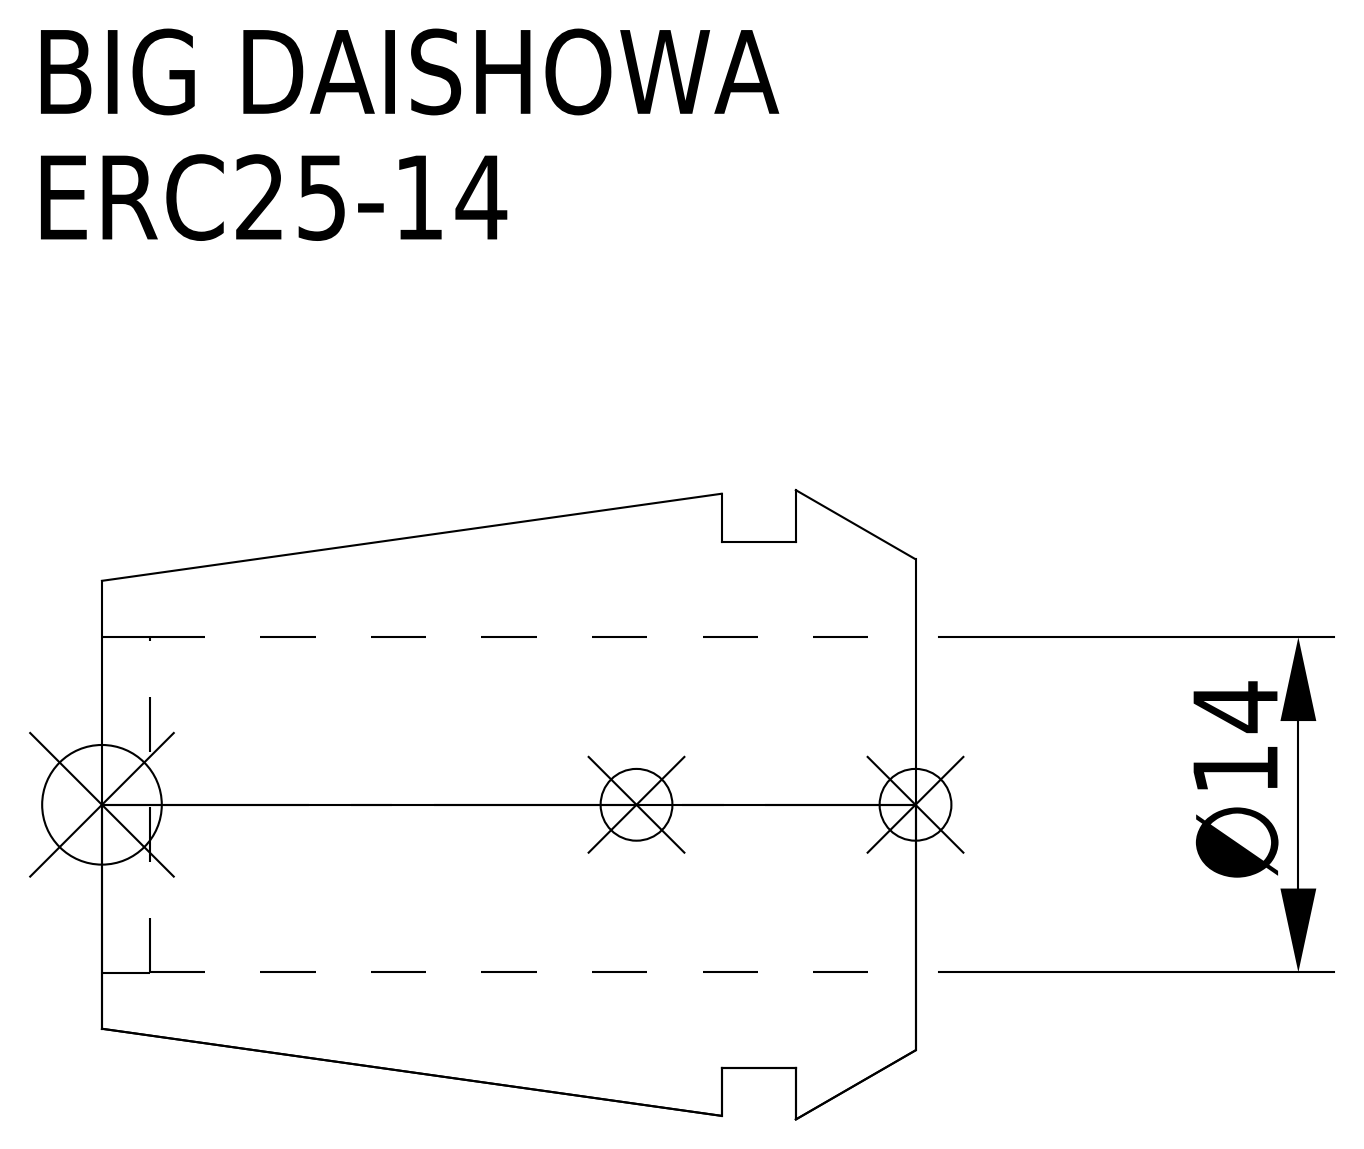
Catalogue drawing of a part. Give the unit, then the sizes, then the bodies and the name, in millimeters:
Units: millimetres
Overall size (bounding box): 34 × 26.3 × 26.3
Round holes (diameter × count): ⌀14 ×1, ⌀14.05 ×1
Round bosses / shafts (diameter × count): ⌀22 ×1
Main face-to-face distances: 5, 8.1, 3.1, 34, 29, 25.9, 32, 27, 23.9, 2
Volume: 8 367 mm³ · Surface area: 4 584 mm²
Bodies: 1 solid, 15 faces (5 planar, 6 cylindrical, 4 other)
Part name (STEP PRODUCT): ERC25-14
STEP written by: CREO PARAMETRIC BY PTC INC, 2016380 (AUTOMOTIVE_DESIGN)
